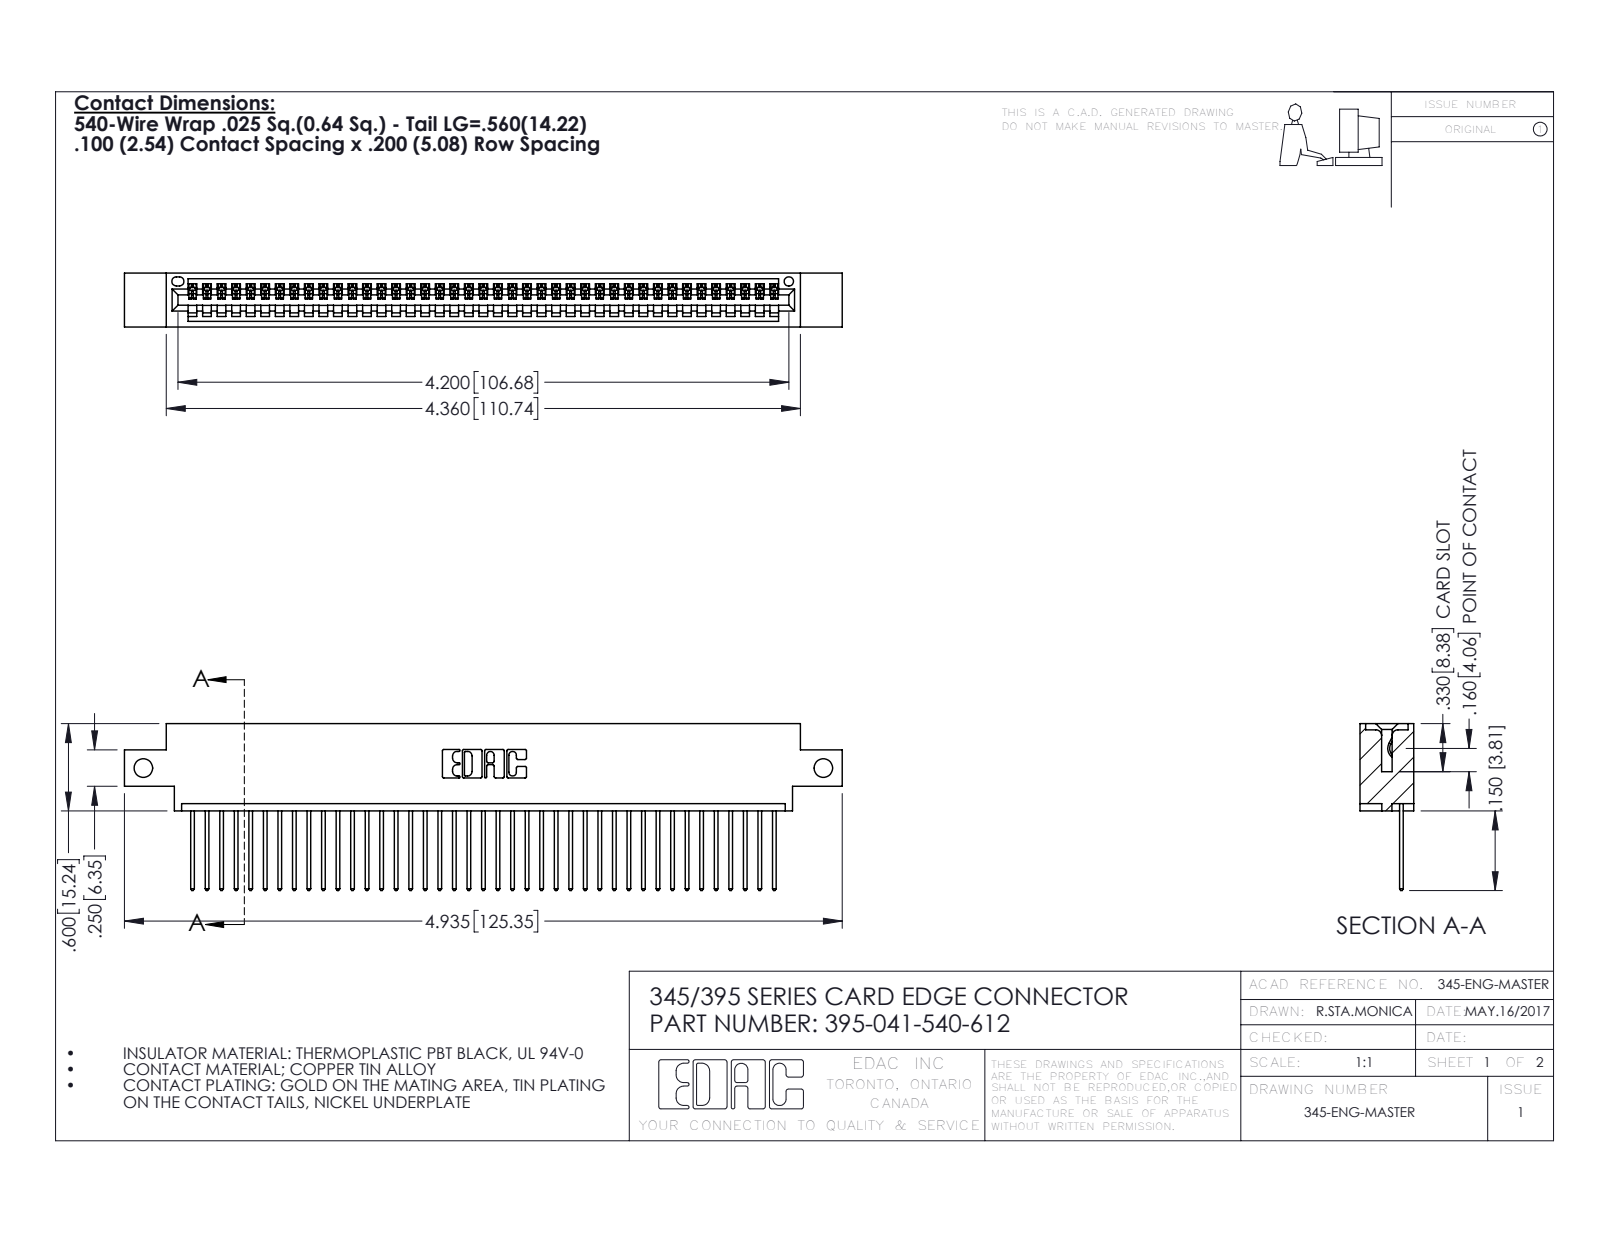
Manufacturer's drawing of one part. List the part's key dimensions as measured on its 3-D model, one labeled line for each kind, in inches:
Part name (STEP PRODUCT): 395-041-540-612; 345-292-001_345-293-140; 345 Part_0.170 Offset - Side Mount
STEP written by: SolidWorks 2016 (CONFIG_CONTROL_DESIGN)
Units: inches
Bodies: 42 solids, 2508 faces (1724 planar, 784 cylindrical, 0 other)
Overall size (bounding box): 4.935 × 1.147 × 0.37
Volume: 0.717 in³ · Surface area: 24.78 in²
Round holes (diameter × count): ⌀0.128 ×2, ⌀0.064 ×1
Partial cylindrical surfaces — rounded edges, fillets, slot ends (radius × count): R0.006 ×82, R0.01 ×82, R0.01 ×22, R0.007 ×6, R0.031 ×6, R0.026 ×3, R0.031 ×2, R0.04 ×2
Main face-to-face distances: 0.298, 0.072, 0.37, 0.098, 0.272, 0.025, 0.2, 0.225, 0.175, 0.149
Hole centre spacings: 4.675
